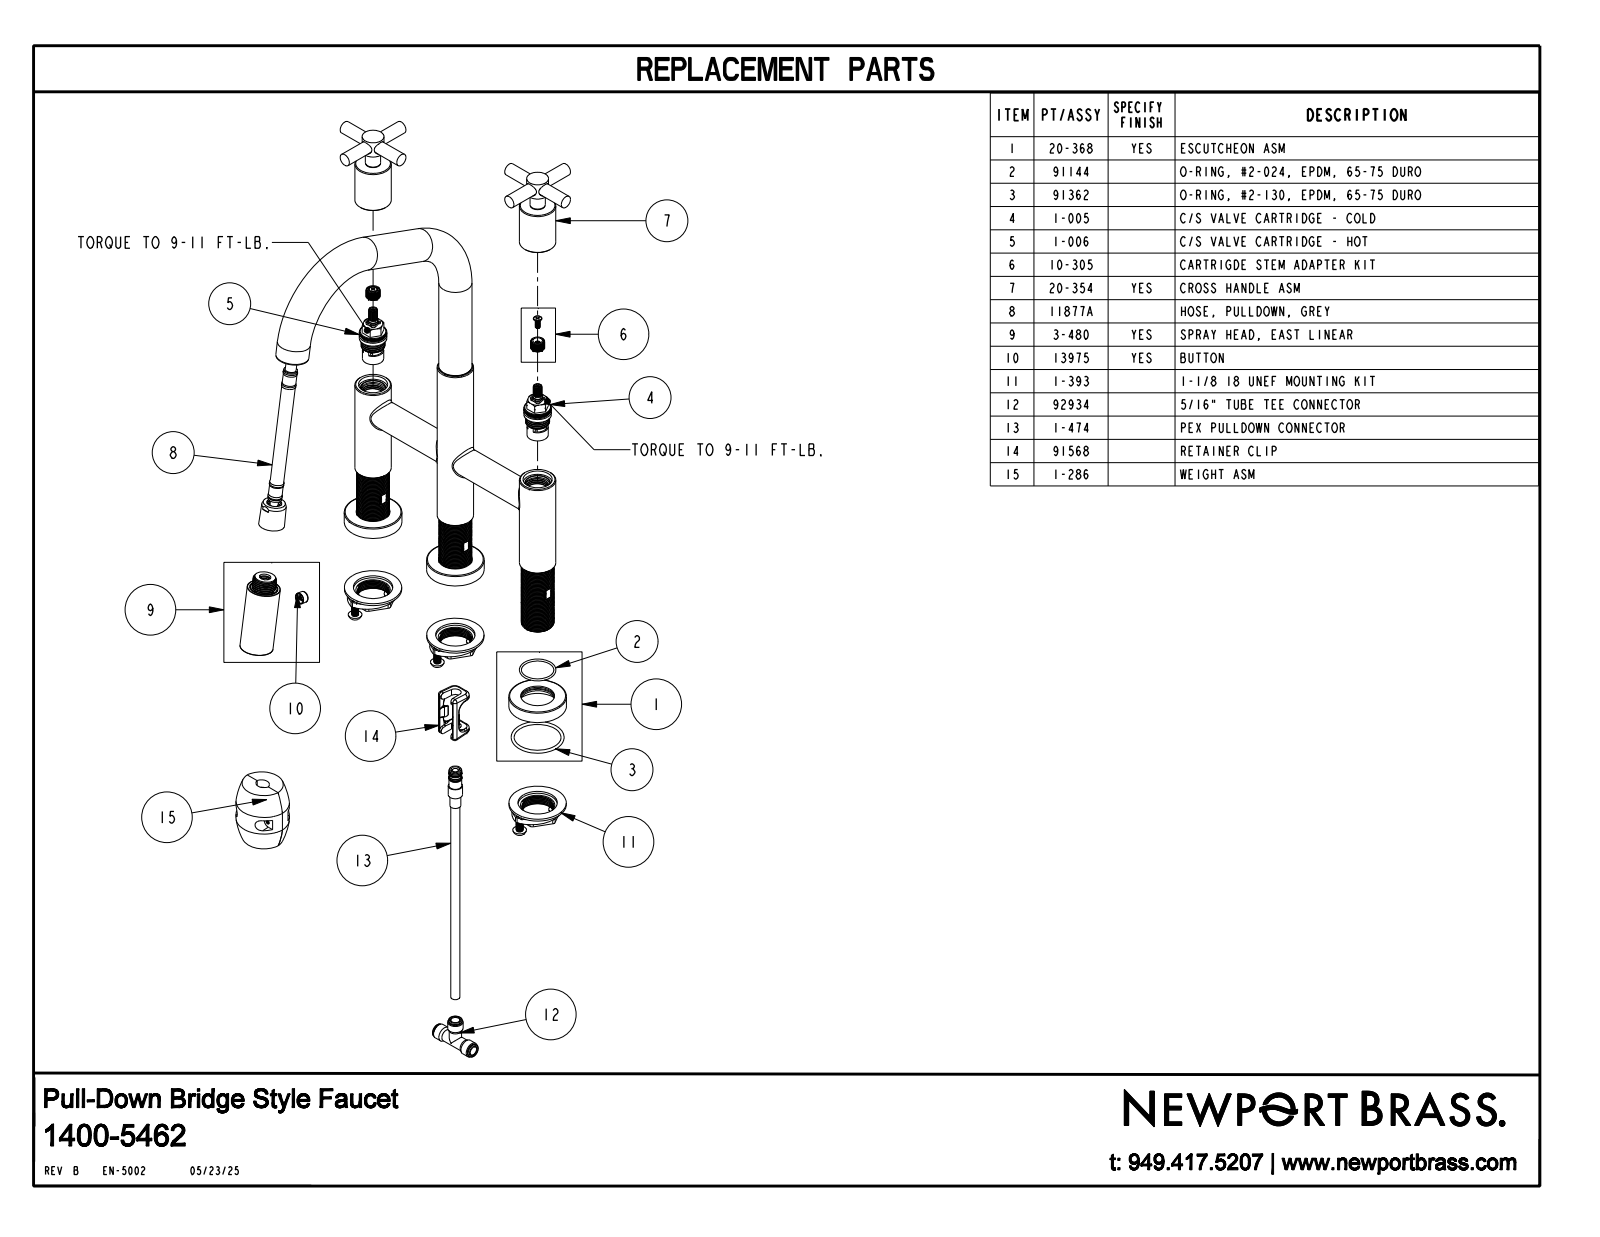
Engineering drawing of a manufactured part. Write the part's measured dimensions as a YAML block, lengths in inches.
part_name: "1400-5462"
step_written_by: "CREO PARAMETRIC BY PTC INC, 2019352 (AUTOMOTIVE_DESIGN)"
units: inches
bodies: {solids: 2, faces: 343, planar: 135, cylindrical: 116, other: 92}
overall_size: [14.34, 10.75, 10.211]
volume: 47.83
surface_area: 186.7
round_holes:
  - {diameter: 0.05, count: 20}
  - {diameter: 0.21, count: 1}
  - {diameter: 0.622, count: 1}
  - {diameter: 0.89, count: 1}
round_bosses_or_shafts:
  - {diameter: 1.14, count: 4}
  - {diameter: 1.98, count: 3}
  - {diameter: 1.25, count: 3}
  - {diameter: 0.445, count: 3}
  - {diameter: 0.75, count: 2}
  - {diameter: 0.525, count: 2}
  - {diameter: 0.506, count: 2}
  - {diameter: 1.124, count: 1}
partial_cylinders:
  - {radius: 0.01, count: 2}
  - {radius: 0.216, count: 2}
  - {radius: 0.53, count: 1}
face_to_face_distances: [0.425, 5.49, 5.065, 6.675, 6.25, 1.185, 6.695, 6.27, 1.205, 0.02]
hole_center_spacings: [0.376, 0.118, 0.232, 0.341, 0.67, 0.442, 0.532, 0.608]
